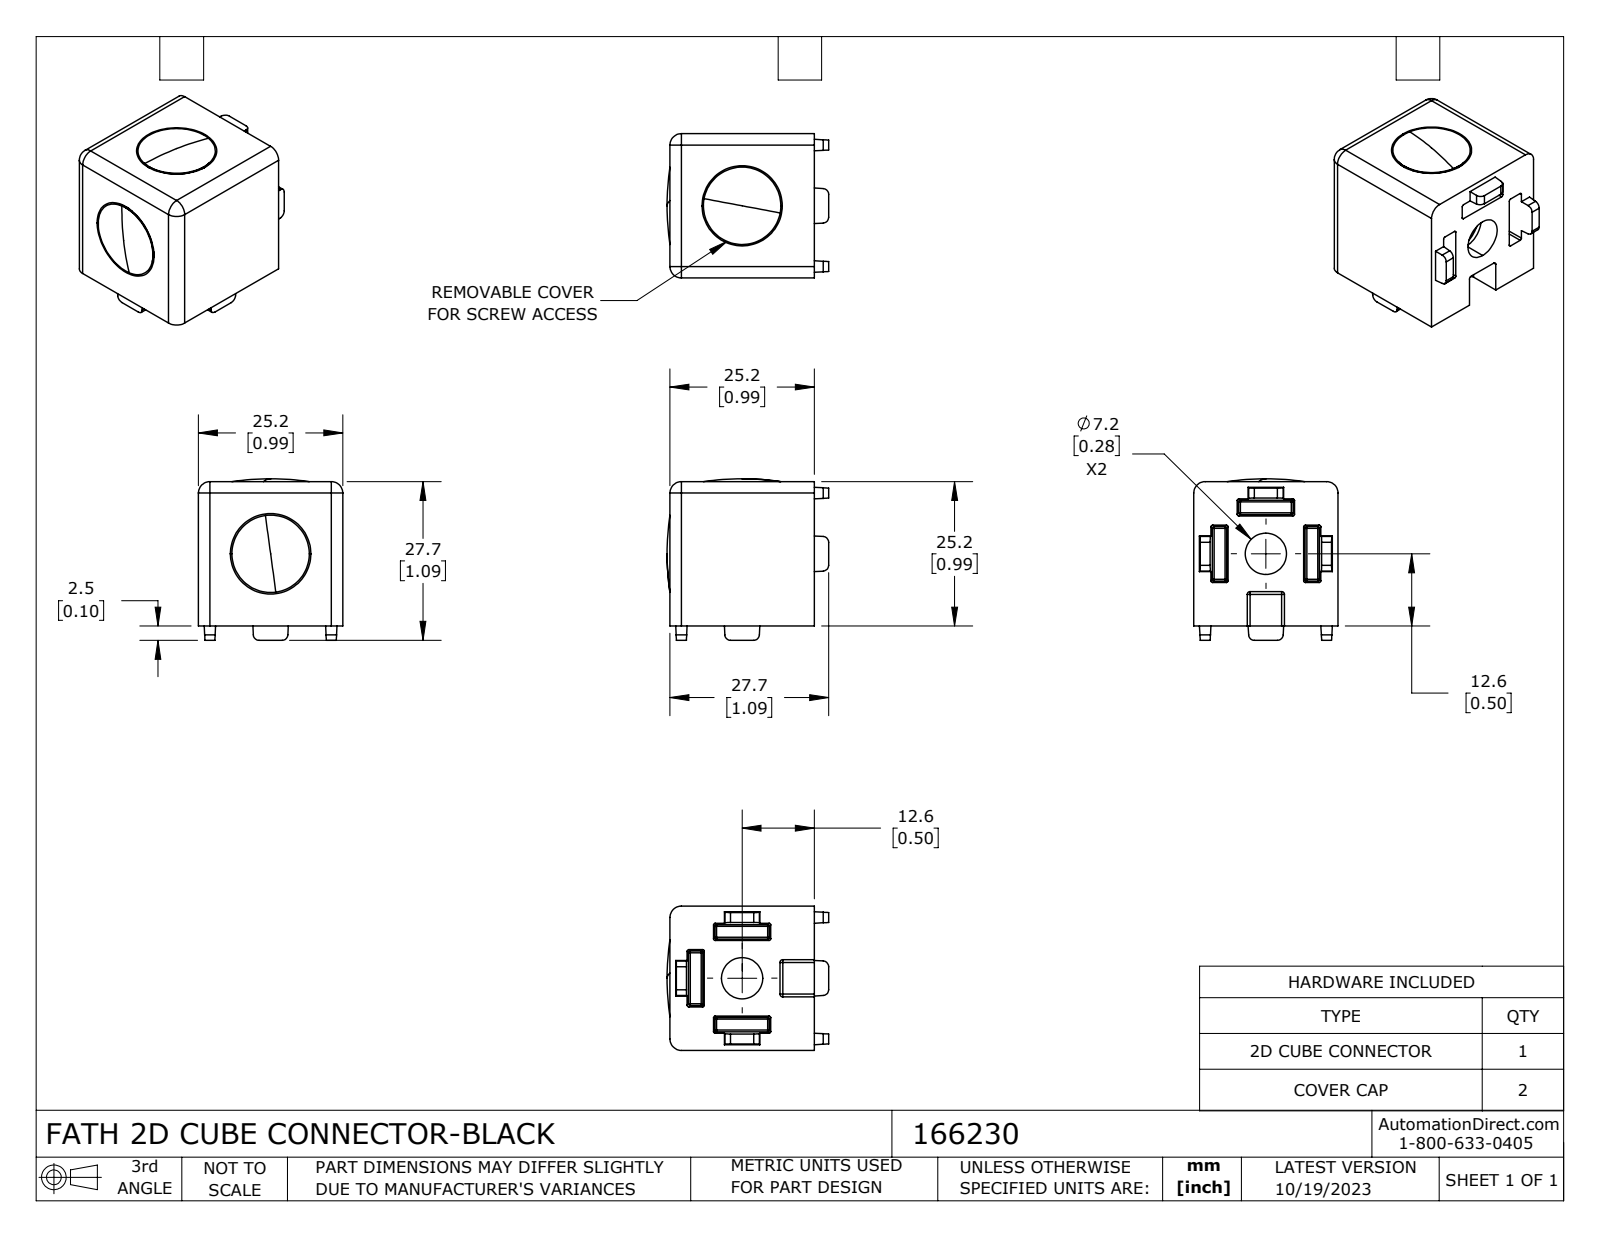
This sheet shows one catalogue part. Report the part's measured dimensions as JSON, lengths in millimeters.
{"part_name": "166230", "step_written_by": "SolidWorks 2023 (CONFIG_CONTROL_DESIGN)", "units": "millimeters", "bodies": {"solids": 3, "faces": 254, "planar": 84, "cylindrical": 96, "other": 74}, "overall_size": [28.2, 28.2, 25.2], "volume_mm3": 11671, "surface_area_mm2": 6635, "round_holes": [[7.2, 2], [11, 2]], "partial_cylinders_radius": [[0.3, 44], [1.2, 12], [1, 8], [0.5, 5], [2, 5]], "face_to_face_distances": [25.2, 5, 16.18, 1, 24.7, 0.5, 4, 21.2, 20.7, 19.7]}
